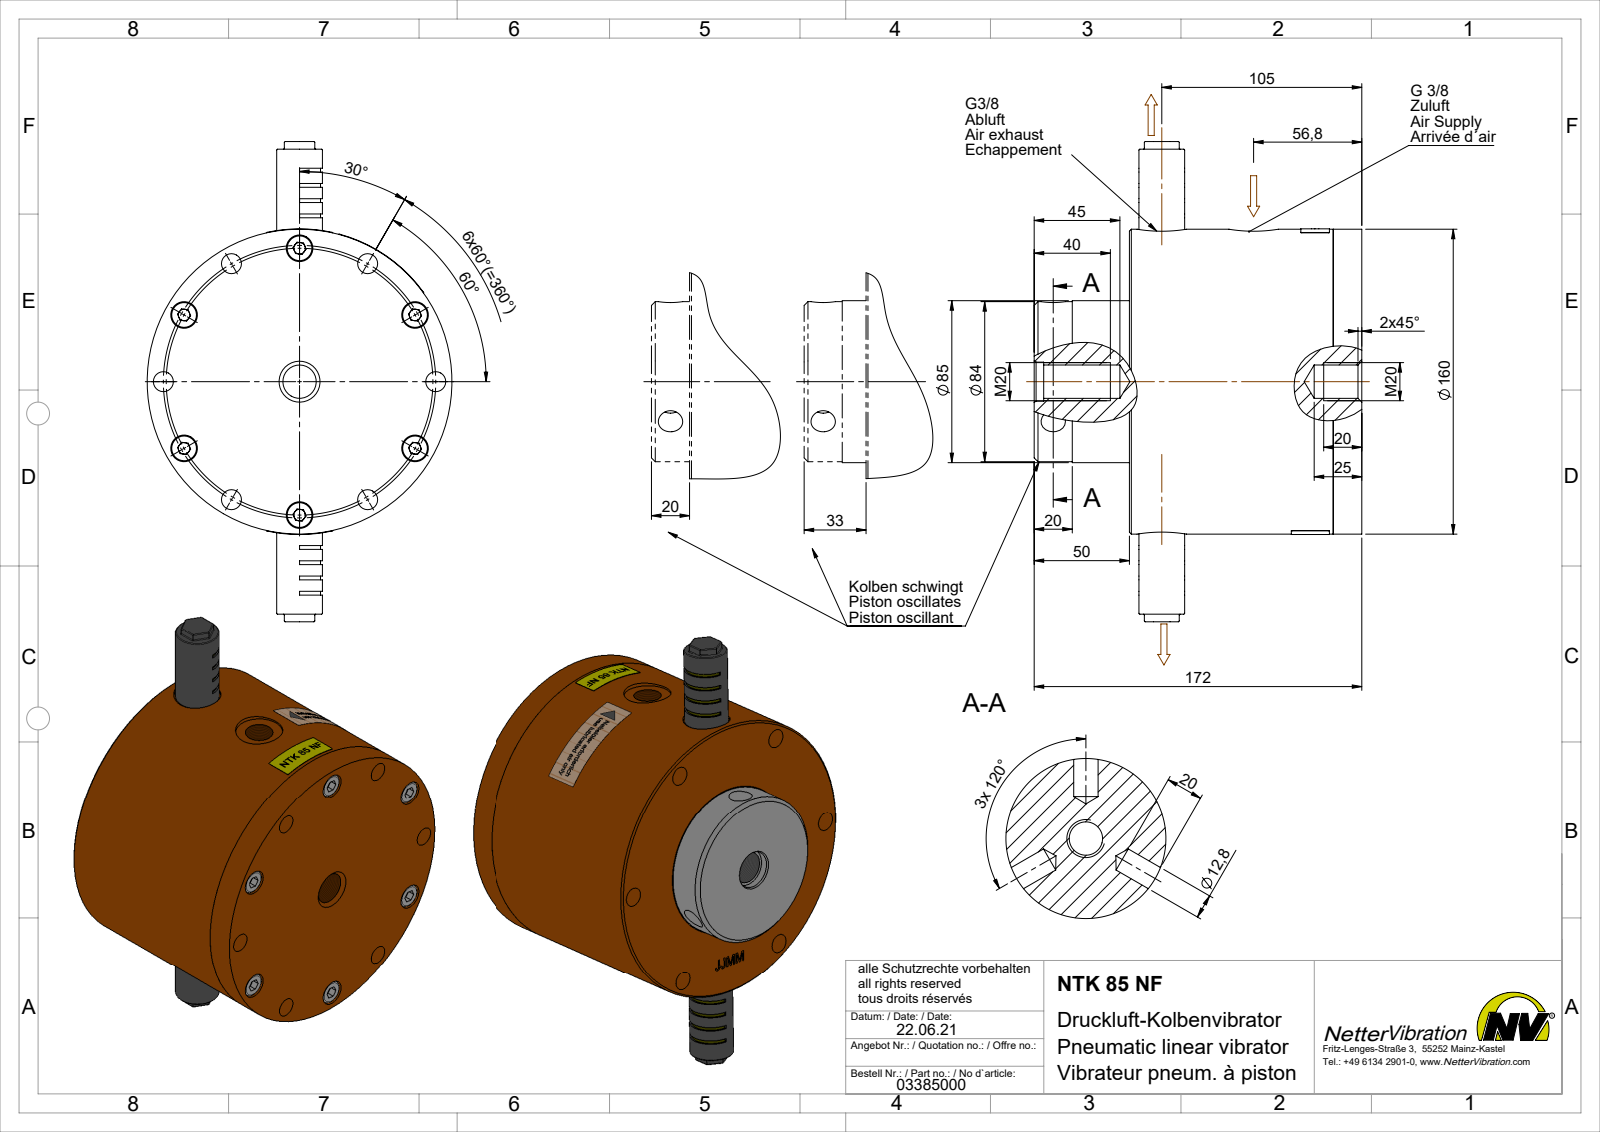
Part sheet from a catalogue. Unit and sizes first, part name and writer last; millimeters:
Units: millimetres
Overall size (bounding box): 252 × 160 × 142
Round holes (diameter × count): ⌀8.5 ×6, ⌀10.5 ×6, ⌀14 ×6, ⌀12.8 ×3, ⌀14.95 ×2, ⌀26 ×2, ⌀17.5 ×1, ⌀85 ×1
Round bosses / shafts (diameter × count): ⌀13 ×6, ⌀8 ×6, ⌀160 ×1, ⌀84 ×1, ⌀24 ×1, ⌀22 ×1, ⌀16.66 ×1
Partial cylindrical surfaces — rounded edges, fillets, slot ends (radius × count): R0.5 ×38, R80.2 ×1
Main face-to-face distances: 15, 107, 122, 45, 65, 3, 62, 60, 42, 57
Hole centre spacings: 36.65, 70, 71.5, 100.06, 136.68, 121.24, 123.84, 140
Volume: 2 524 000 mm³ · Surface area: 245 413 mm²
Bodies: 13 solids, 575 faces (167 planar, 270 cylindrical, 138 other)
Part name (STEP PRODUCT): NTK 85 NF #03385000
STEP written by: SolidWorks 2015 (AUTOMOTIVE_DESIGN)
